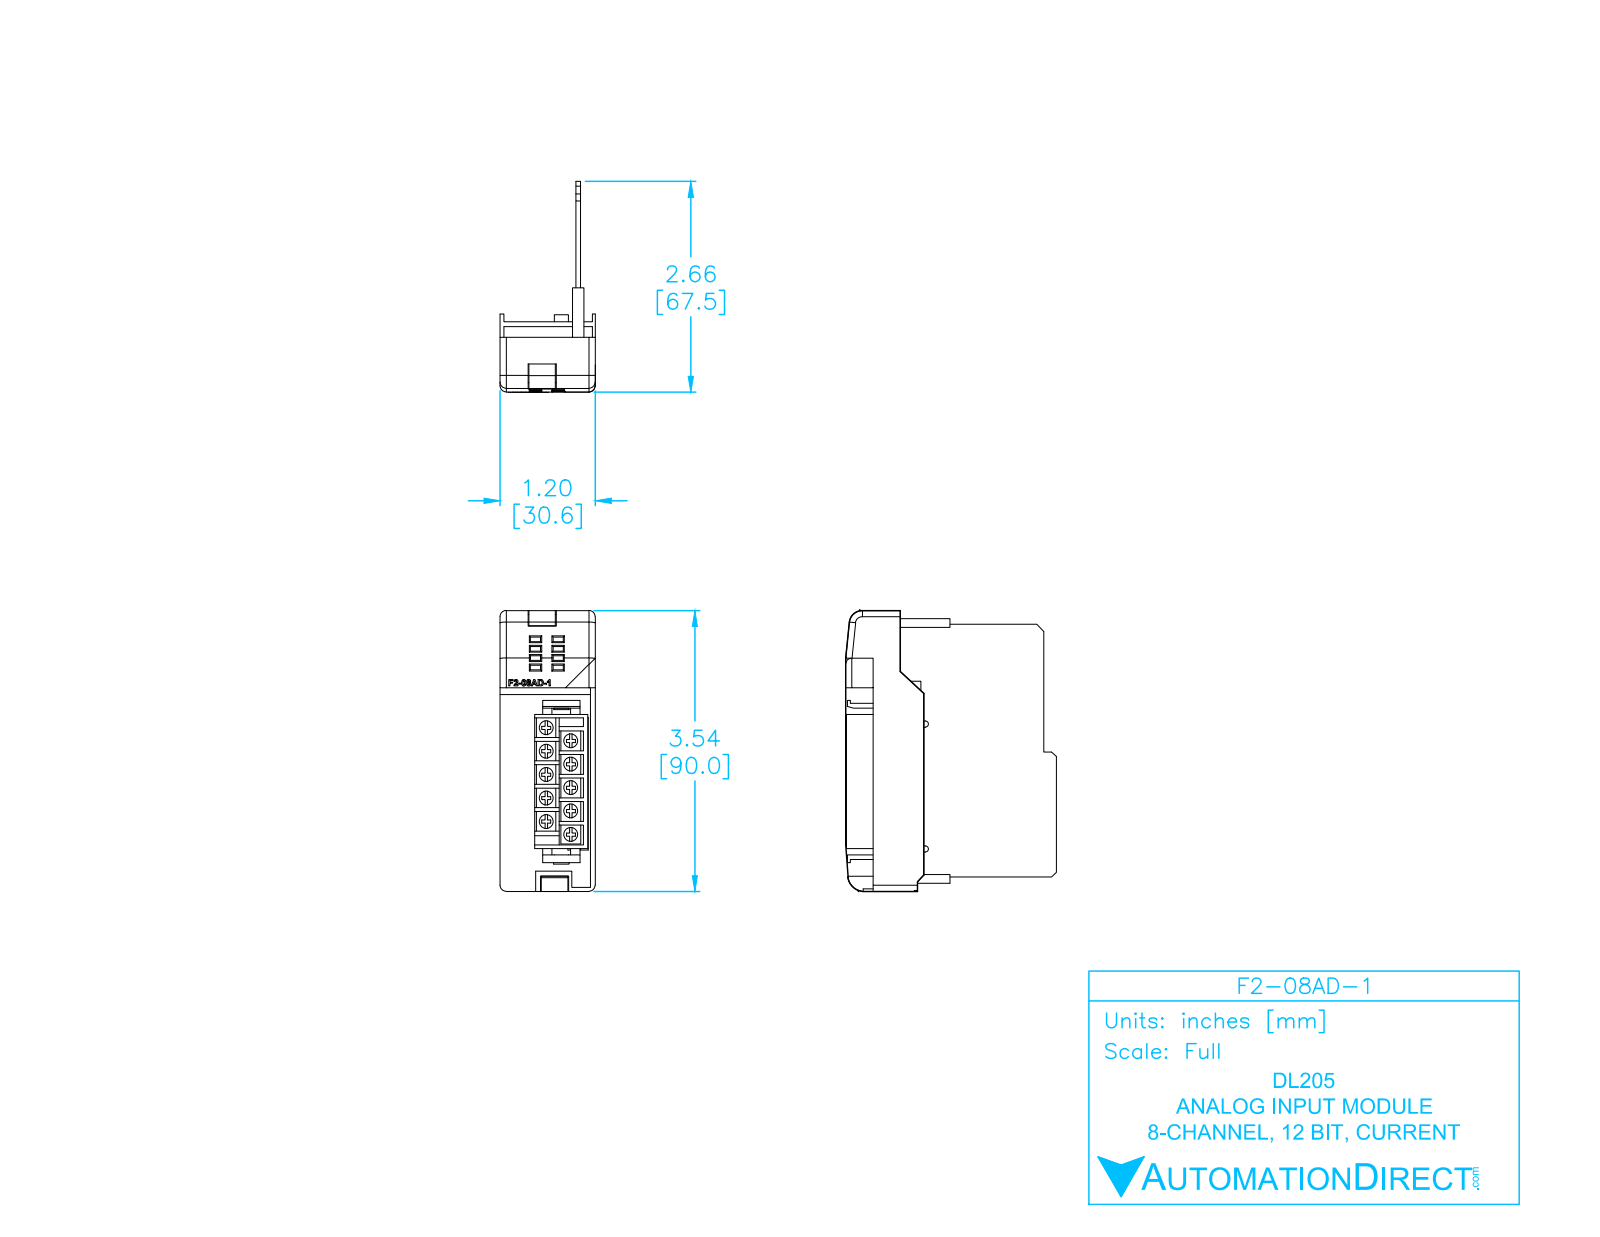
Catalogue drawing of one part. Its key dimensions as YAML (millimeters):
part_name: "F2-08AD-1_ModuleCase_light_NEW"
step_written_by: "SolidWorks 2009 (AUTOMOTIVE_DESIGN)"
units: millimeters
bodies: {solids: 6, faces: 580, planar: 412, cylindrical: 75, other: 93}
overall_size: [90, 67.61, 30.55]
volume: 25374
surface_area: 28532
round_bosses_or_shafts:
  - {diameter: 4.5, count: 10}
partial_cylinders:
  - {radius: 0.35, count: 16}
  - {radius: 2, count: 9}
  - {radius: 0.25, count: 2}
  - {radius: 1, count: 2}
  - {radius: 1.25, count: 2}
  - {radius: 4.12, count: 1}
  - {radius: 5.39, count: 1}
face_to_face_distances: [1.5, 4.72, 6.22, 3.62, 2.12, 2.6, 3.22, 1.1, 7.25, 8.14]
